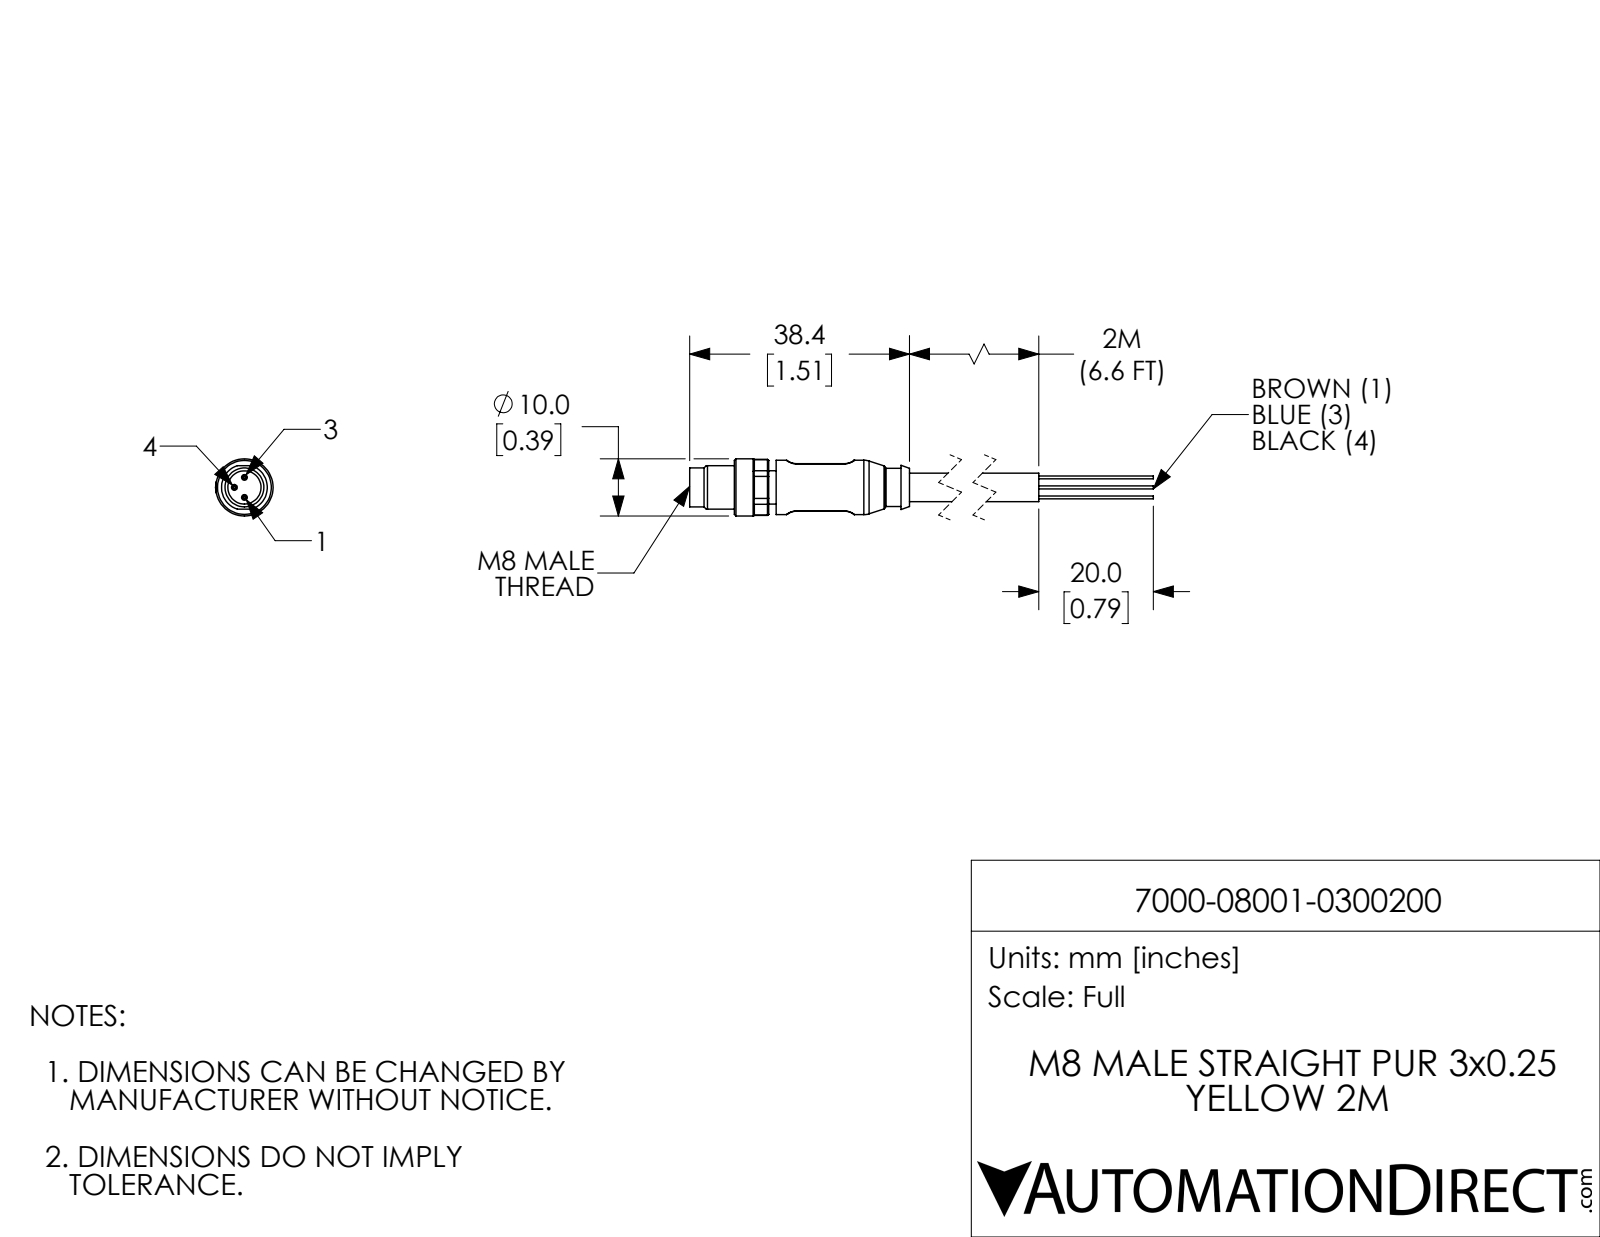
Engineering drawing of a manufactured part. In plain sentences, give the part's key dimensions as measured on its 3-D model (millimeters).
The part is named "7000-08001-0300200". Its 3-D file was written by "SolidWorks 2021 (CONFIG_CONTROL_DESIGN)". It is 4 solids with 119 faces: 41 planar, 44 cylindrical and 34 other. Overall it measures 78.4 by 10.05 by 10 millimeters. Its volume is 2 535 cubic millimeters and its surface area 1 801 square millimeters. Round holes: 1 of diameter 5.8. Round bosses or shafts: 3 of diameter 1, 3 of diameter 0.51, 1 of diameter 10, 1 of diameter 9.5, 1 of diameter 8, 1 of diameter 6.8, 1 of diameter 6.7, 1 of diameter 5. Partial cylindrical surfaces (rounded edges, fillets, slot ends): 4 of radius 0.2, 4 of radius 2.5, 1 of radius 4.9, 1 of radius 5.05. The main face-to-face distances are 8.3, 1.3, 9, 0.35, 7.95, 8.8, 10.1, 53.4, 44.6, 43.3.
